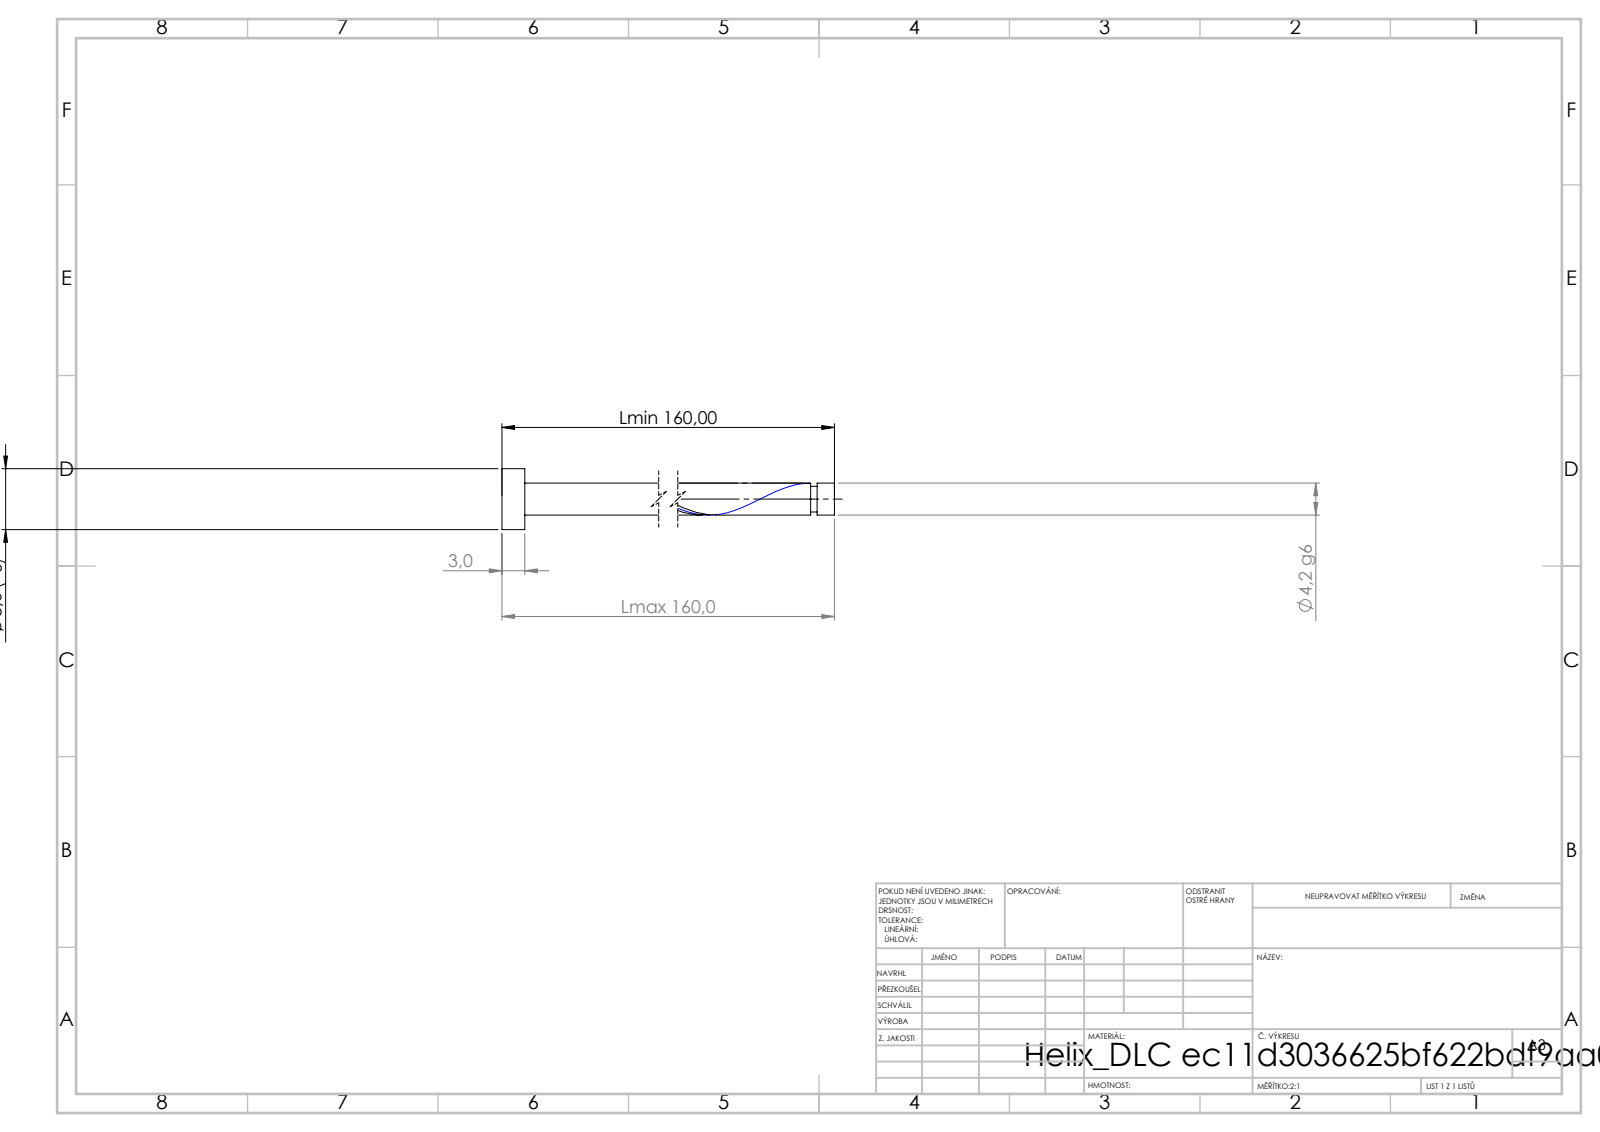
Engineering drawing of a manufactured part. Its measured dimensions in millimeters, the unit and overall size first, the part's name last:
Units: millimetres
Overall size (bounding box): 160 × 8 × 8
Round bosses / shafts (diameter × count): ⌀8 ×1, ⌀4.2 ×1, ⌀3.36 ×1
Main face-to-face distances: 3, 160, 157, 157.72, 154.72, 2.28, 156.88, 153.88, 0.84, 3.12
Volume: 2 301 mm³ · Surface area: 2 292 mm²
Bodies: 1 solid, 21 faces (6 planar, 14 cylindrical, 1 other)
STEP written by: SolidWorks 2019 (CONFIG_CONTROL_DESIGN)
